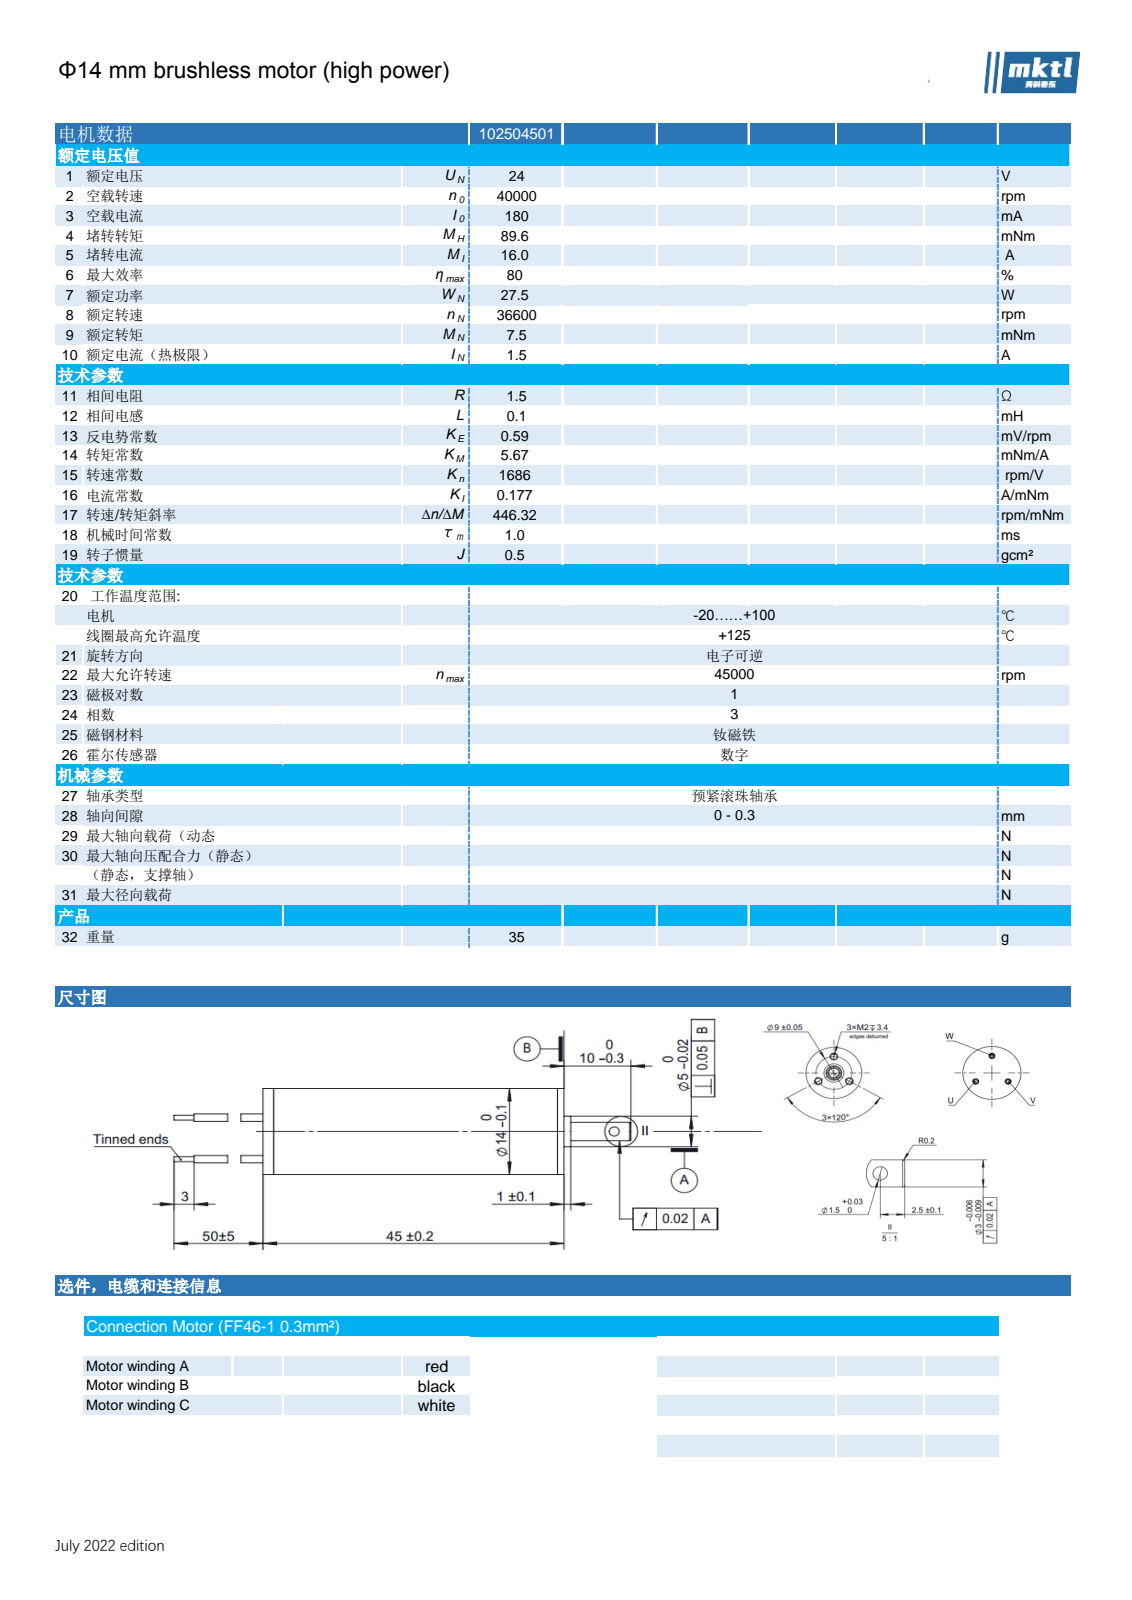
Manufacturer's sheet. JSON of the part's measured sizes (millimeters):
{"part_name": "102504501", "step_written_by": "SolidWorks 2025 (AUTOMOTIVE_DESIGN)", "units": "millimeters", "bodies": {"solids": 184, "faces": 1201, "planar": 389, "cylindrical": 764, "other": 48}, "overall_size": [68.3, 14, 14], "volume_mm3": 6376, "surface_area_mm2": 31647, "round_holes": [[1.5, 4], [1.6, 3], [3, 1], [3.1, 1], [4, 1], [5.2, 1], [6, 1], [7, 1], [7.1, 1], [9.8, 1], [10, 1], [10.2, 1]], "round_bosses_or_shafts": [[1.2, 3], [0.8, 3], [0.58, 3], [14, 1], [13.2, 1], [13.1, 1], [6.6, 1], [6.4, 1]], "face_to_face_distances": [0.4, 0.6, 0.8, 1, 1.2, 1.4, 1.6, 1.8, 2, 2.2], "hole_center_spacings": [4.5, 7.8, 9]}
